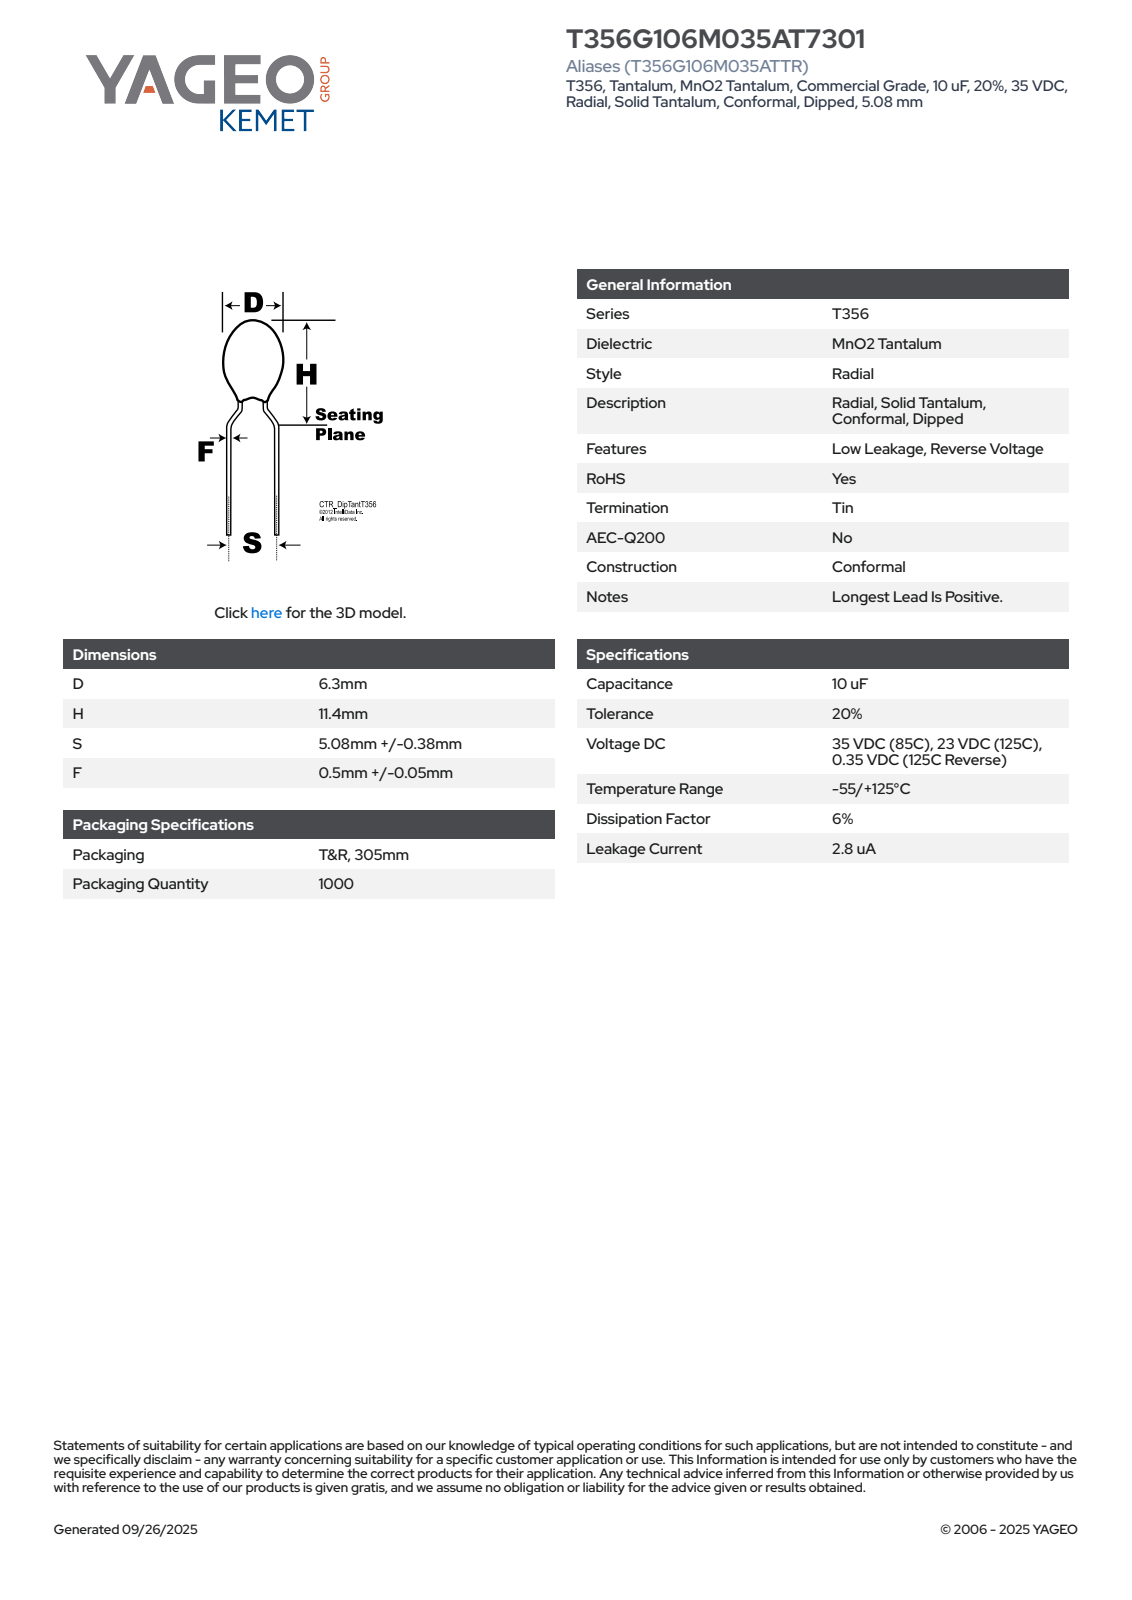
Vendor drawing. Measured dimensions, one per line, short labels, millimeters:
name: CTR_T356_D6.3H11.4S5.08LL5.56F0.55
written by: SolidWorks 2014 (AUTOMOTIVE_DESIGN)
unit: mm
bodies: 1 solid, 96 faces (27 planar, 18 cylindrical, 51 other)
size: 16.96 × 6.3 × 6.3
volume: 224 mm³; area: 219 mm²
bosses: 6× ⌀0.55, 1× ⌀6.3
rounds: 1× R3.14
face distances: 7.95, 9.01, 16.96, 14.2, 5.19, 2.76, 13.3, 4.29, 0.9, 3.66
